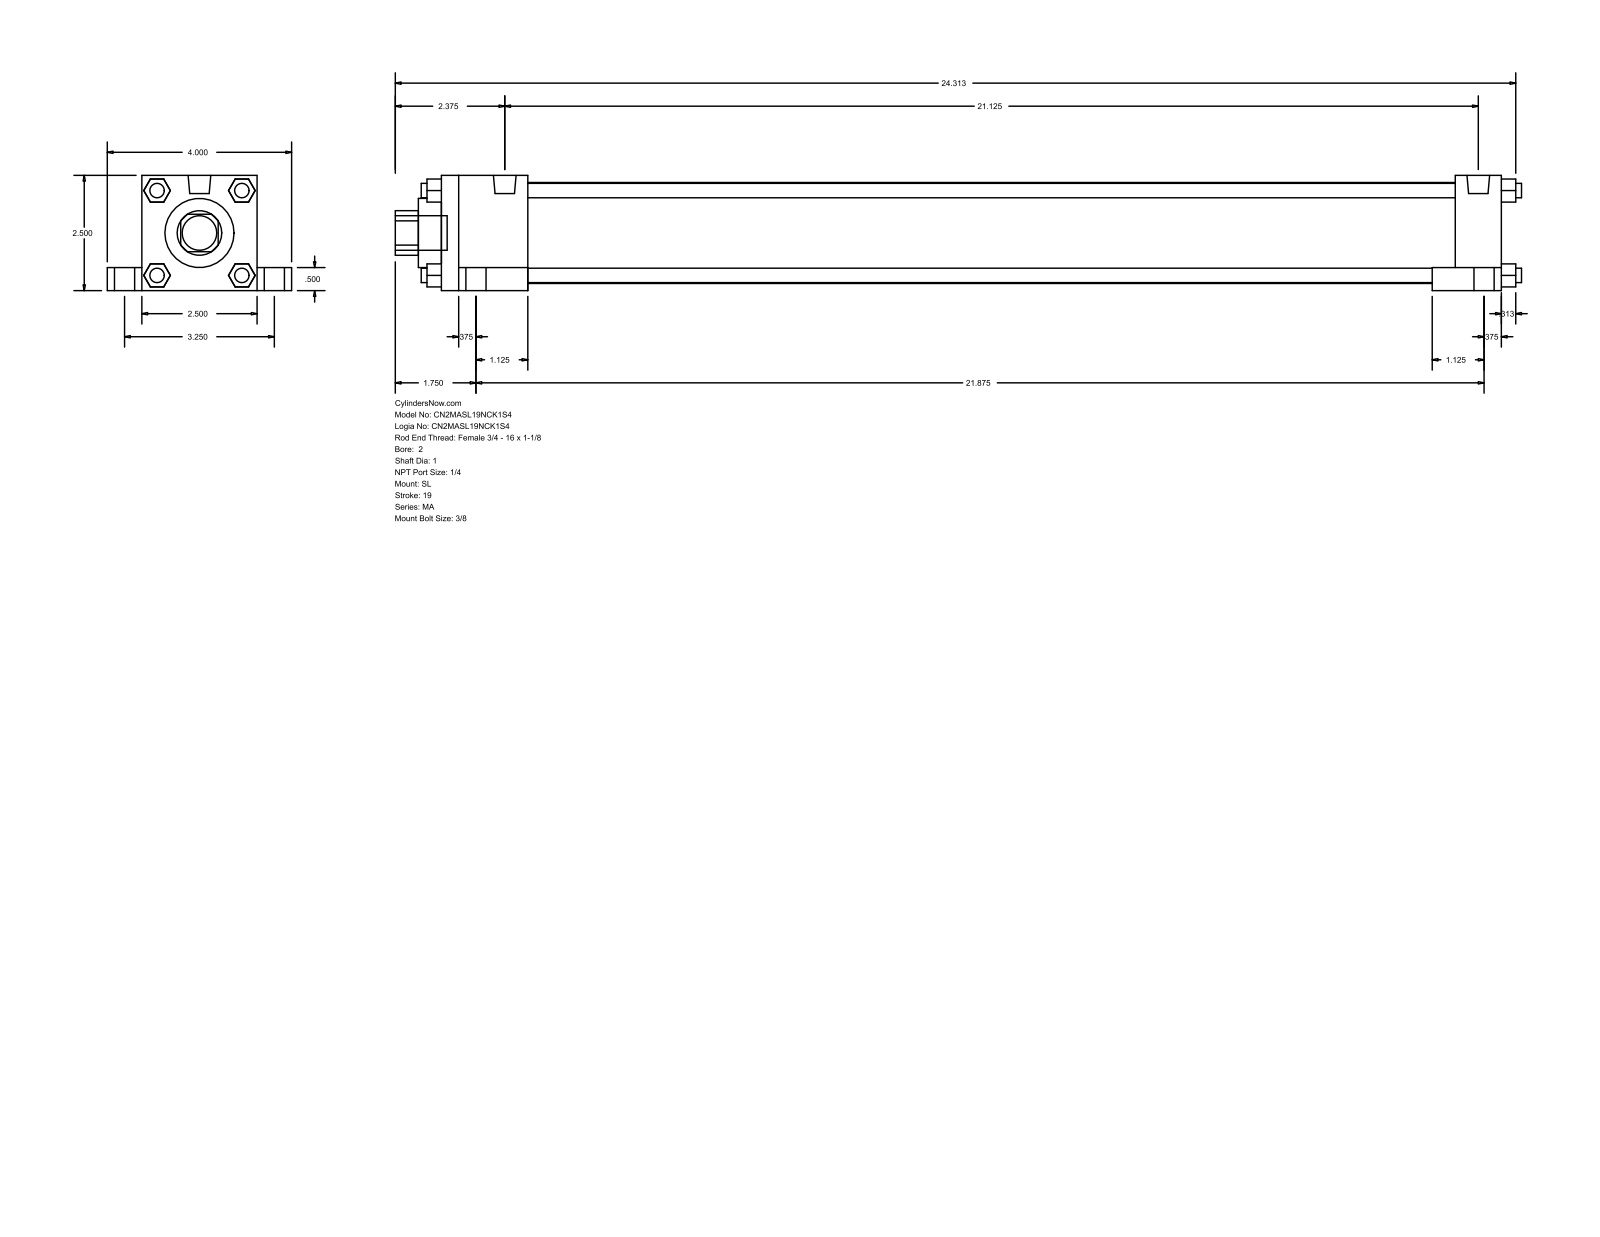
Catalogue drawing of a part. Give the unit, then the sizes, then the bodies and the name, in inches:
Units: inches
Overall size (bounding box): 24.437 × 4 × 2.5
Round holes (diameter × count): ⌀1 ×1, ⌀1.5 ×1, ⌀2.19 ×1
Round bosses / shafts (diameter × count): ⌀0.313 ×8, ⌀0.687 ×4, ⌀0.437 ×4, ⌀0.492 ×2, ⌀0.75 ×1
Partial cylindrical surfaces — rounded edges, fillets, slot ends (radius × count): R0.484 ×1
Main face-to-face distances: 2.5, 0.5, 23, 0.75, 3.25, 1, 2, 1.875, 21.125, 22
Bodies: 0 solids, 148 faces (112 planar, 36 cylindrical, 0 other)
Part name (STEP PRODUCT): MA_SL__0200_1
STEP written by: GSSL Pune (CONFIG_CONTROL_DESIGN)
